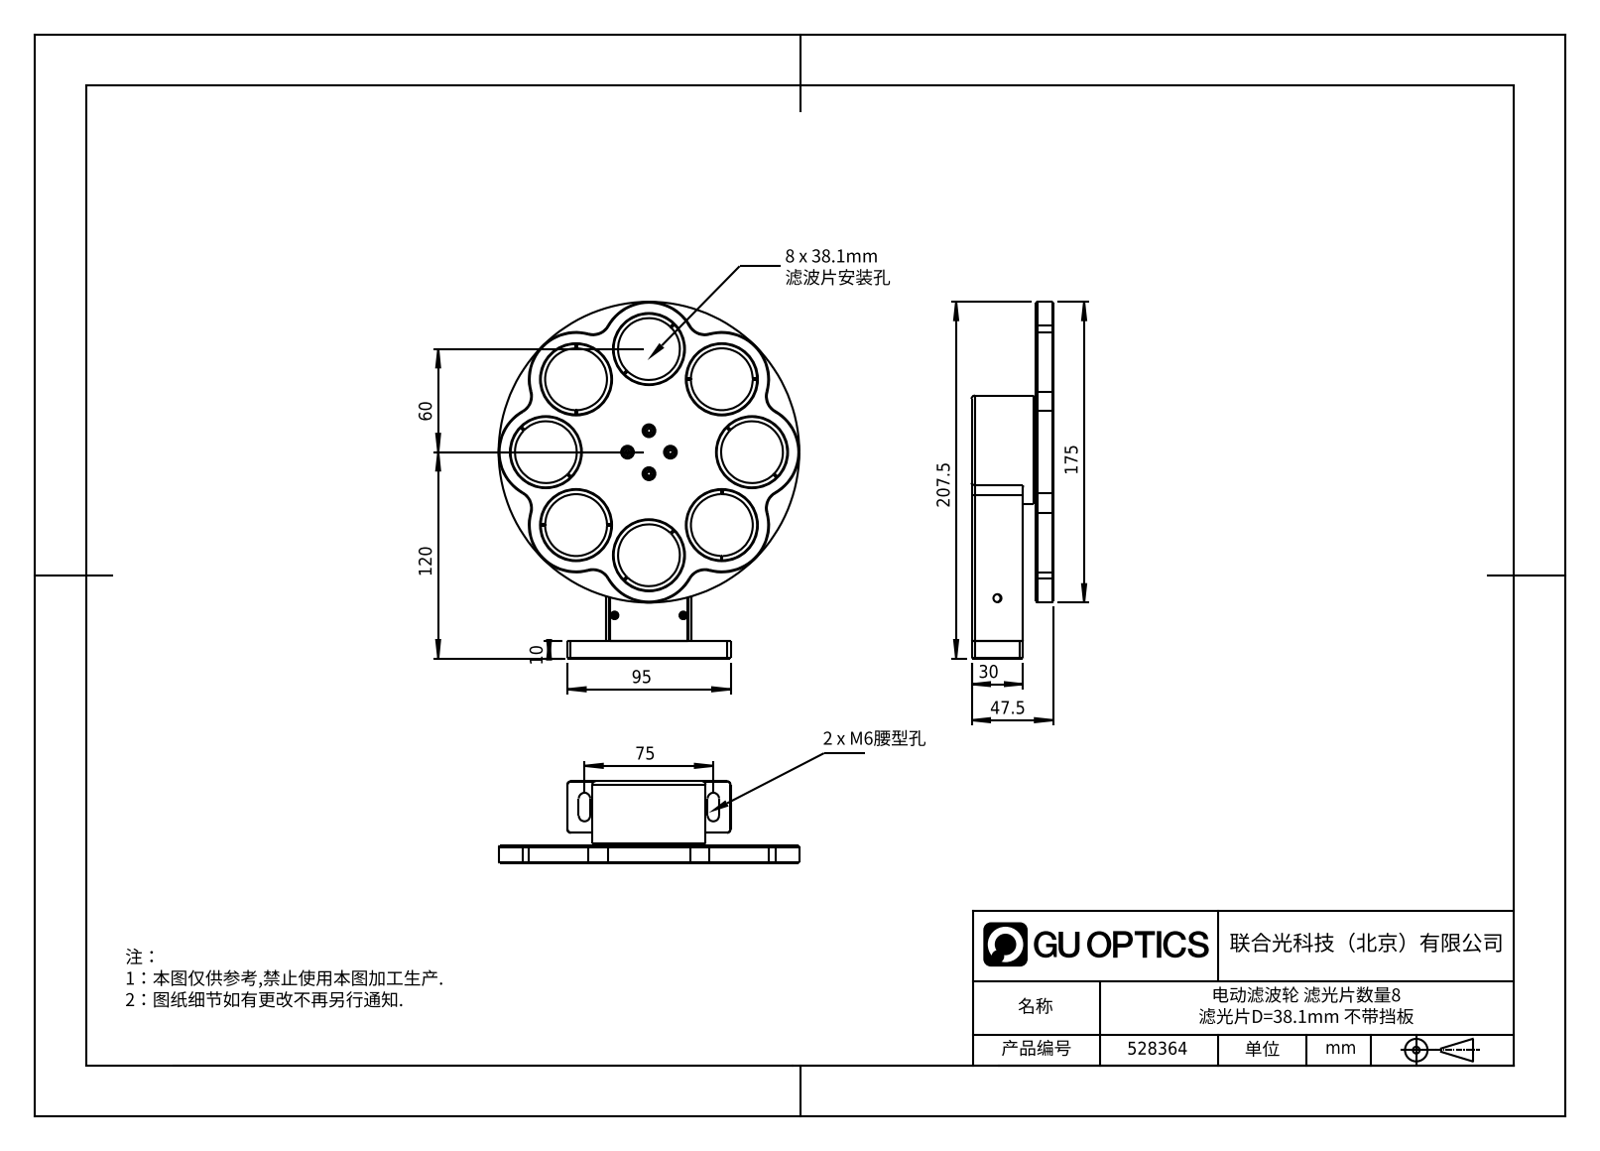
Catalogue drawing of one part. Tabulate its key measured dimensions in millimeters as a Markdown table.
| quantity | value |
| --- | --- |
| part name | 528364 |
| STEP written by | SolidWorks 2020 (CONFIG_CONTROL_DESIGN) |
| units | millimeters |
| bodies | 0 solids, 380 faces (217 planar, 67 cylindrical, 96 other) |
| overall size | 207.5 × 175 × 47.5 |
| round holes (diameter × count) | 8 × 4, 66 × 1, 175 × 1 |
| round bosses / shafts (diameter × count) | 36 × 8, 6.5 × 8, 41 × 4, 5.5 × 3, 4.4 × 2, 4.7 × 1 |
| partial cylindrical surfaces (radius × count) | 10 × 10, 27.5 × 8, 2 × 6, 3.3 × 4 |
| main face-to-face distances | 10, 1, 9, 6, 5, 4, 37.5, 38.5, 43.5, 47.5 |
| hole center spacings | 18, 42, 45.69 |
